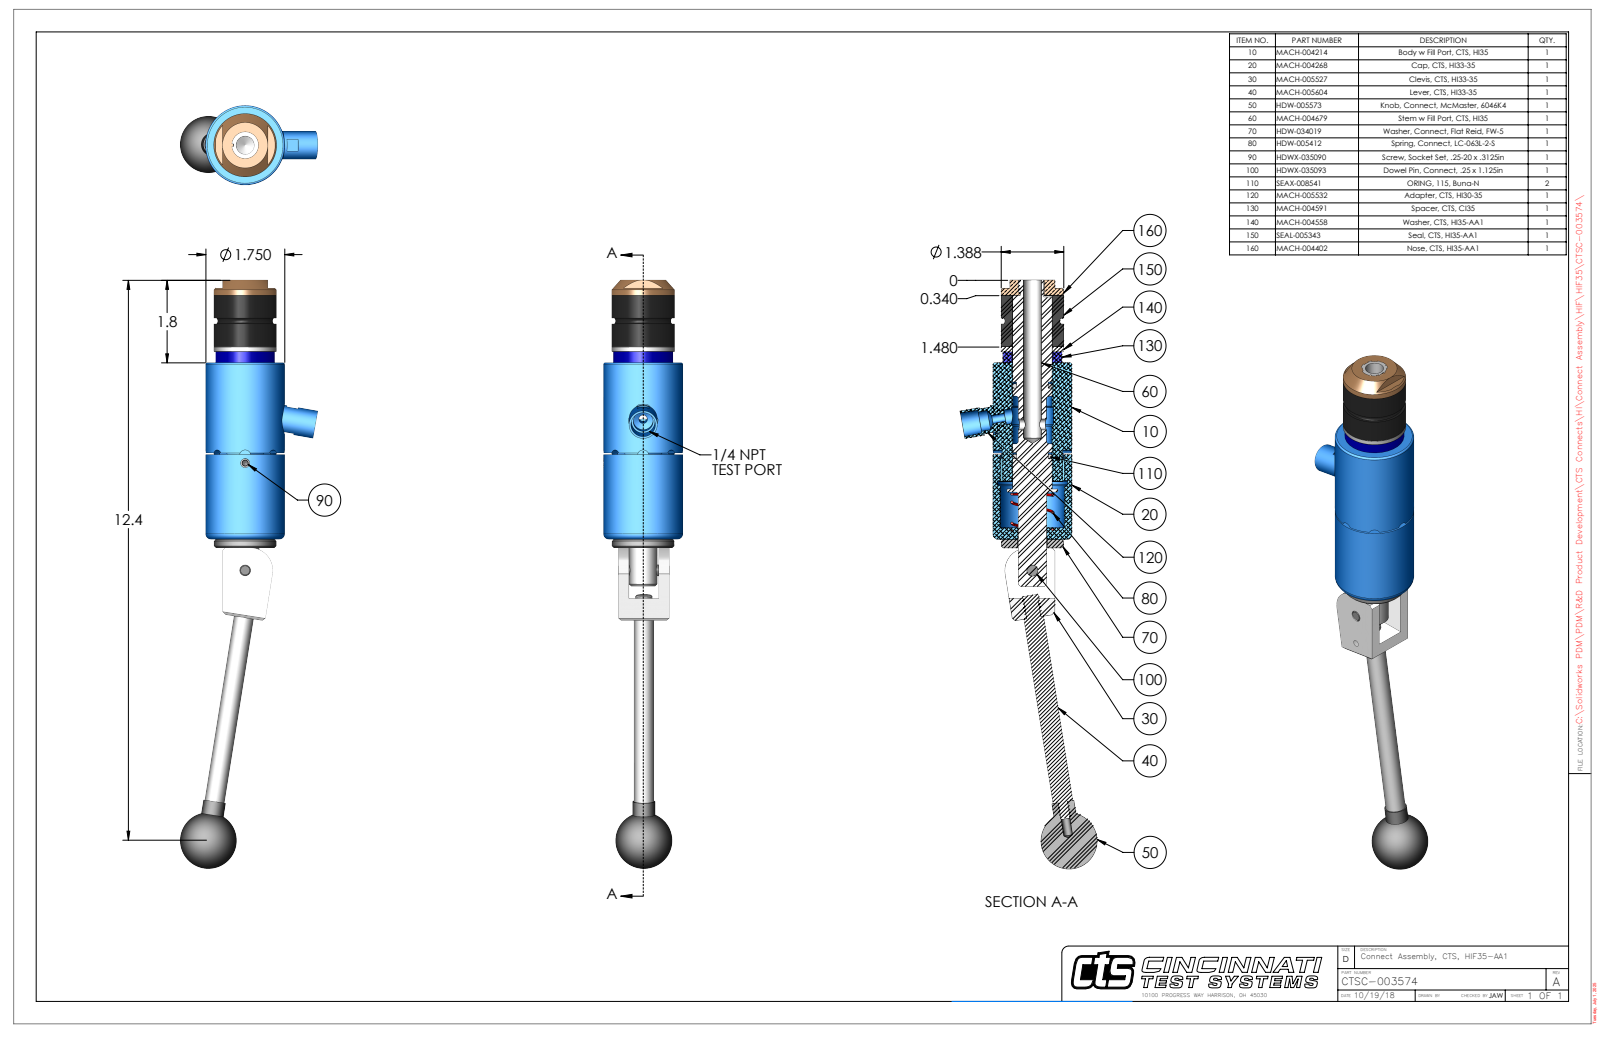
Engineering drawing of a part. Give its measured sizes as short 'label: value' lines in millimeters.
name: CTSC-003574
written by: SolidWorks 2023 (AUTOMOTIVE_DESIGN)
unit: mm
bodies: 11 solids, 296 faces (109 planar, 121 cylindrical, 66 other)
size: 331.3 × 77.3 × 44.5
volume: 242 700 mm³; area: 59 230 mm²
holes: 2× ⌀5.1, 1× ⌀3.8, 1× ⌀4.7, 1× ⌀6.3, 1× ⌀6.4, 1× ⌀6.4, 1× ⌀8, 1× ⌀10.3, 1× ⌀11.1, 1× ⌀13.5, 1× ⌀16.1, 1× ⌀16.7
bosses: 2× ⌀6.4, 1× ⌀44.5, 1× ⌀35.3, 1× ⌀35.1, 1× ⌀33.3, 1× ⌀22.1, 1× ⌀15.9, 1× ⌀15.7
rounds: 4× R3.2, 2× R0.7, 1× R6.1, 1× R8.4, 1× R12.7, 1× R17.7, 1× R20.8
face distances: 99.4, 37.8, 137.3, 29, 8.9, 108.3, 31.8, 2.8, 6.1, 105.5
hole spacings: 18.8, 60.4, 79.1
